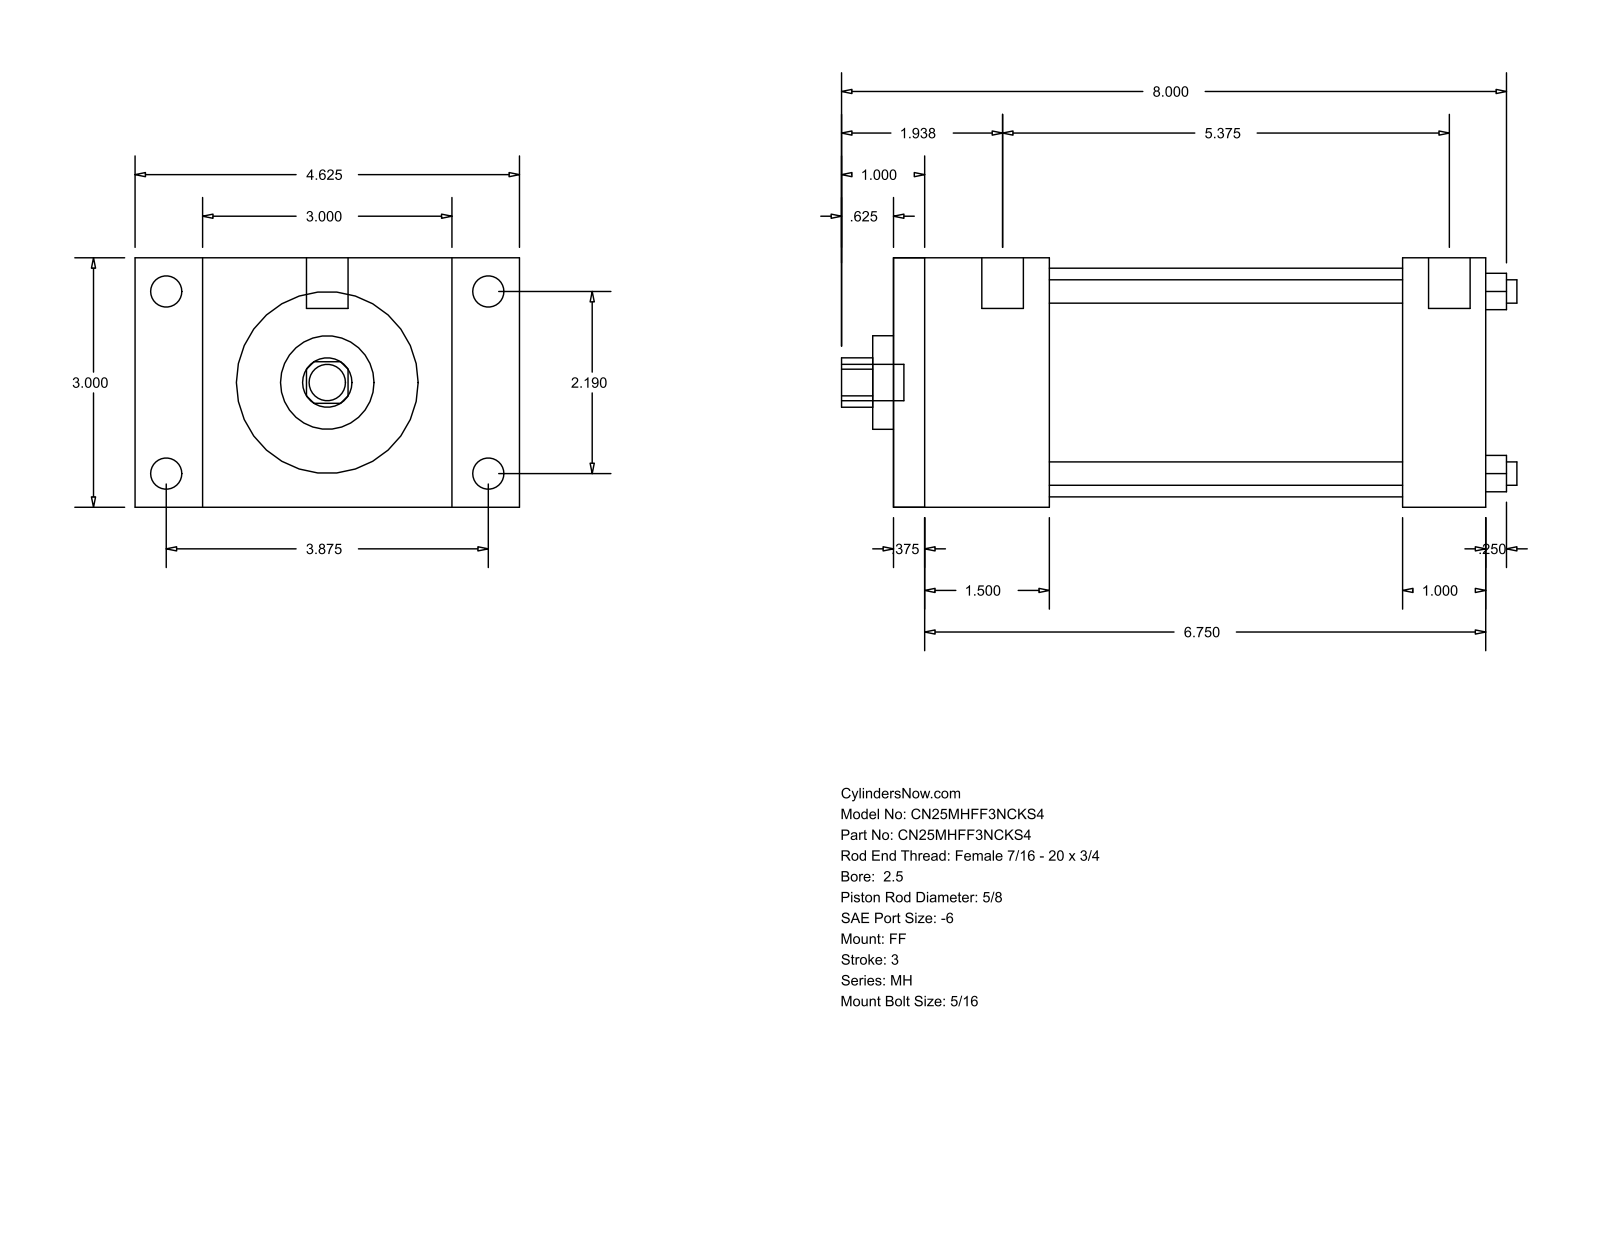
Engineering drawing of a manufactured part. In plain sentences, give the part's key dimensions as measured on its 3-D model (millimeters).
The part is named "MH_FF__0250_0.625". Its 3-D file was written by "GSSL Pune (CONFIG_CONTROL_DESIGN)". It is 0 solids with 92 faces: 64 planar, 28 cylindrical and 0 other. Overall it measures 206.38 by 117.47 by 76.2 millimeters. Round holes: 4 of diameter 7.14, 1 of diameter 15.88, 1 of diameter 28.57, 1 of diameter 69.85. Round bosses or shafts: 4 of diameter 9.53, 4 of diameter 5.56, 2 of diameter 12.7, 1 of diameter 11.11. Partial cylindrical surfaces (rounded edges, fillets, slot ends): 1 of radius 7.54. The main face-to-face distances are 76.2, 180.97, 9.52, 171.45, 25.4, 47.62, 155.57, 38.1, 146.05, 107.95. The hole center spacings are 39.33, 55.62, 78.66.
